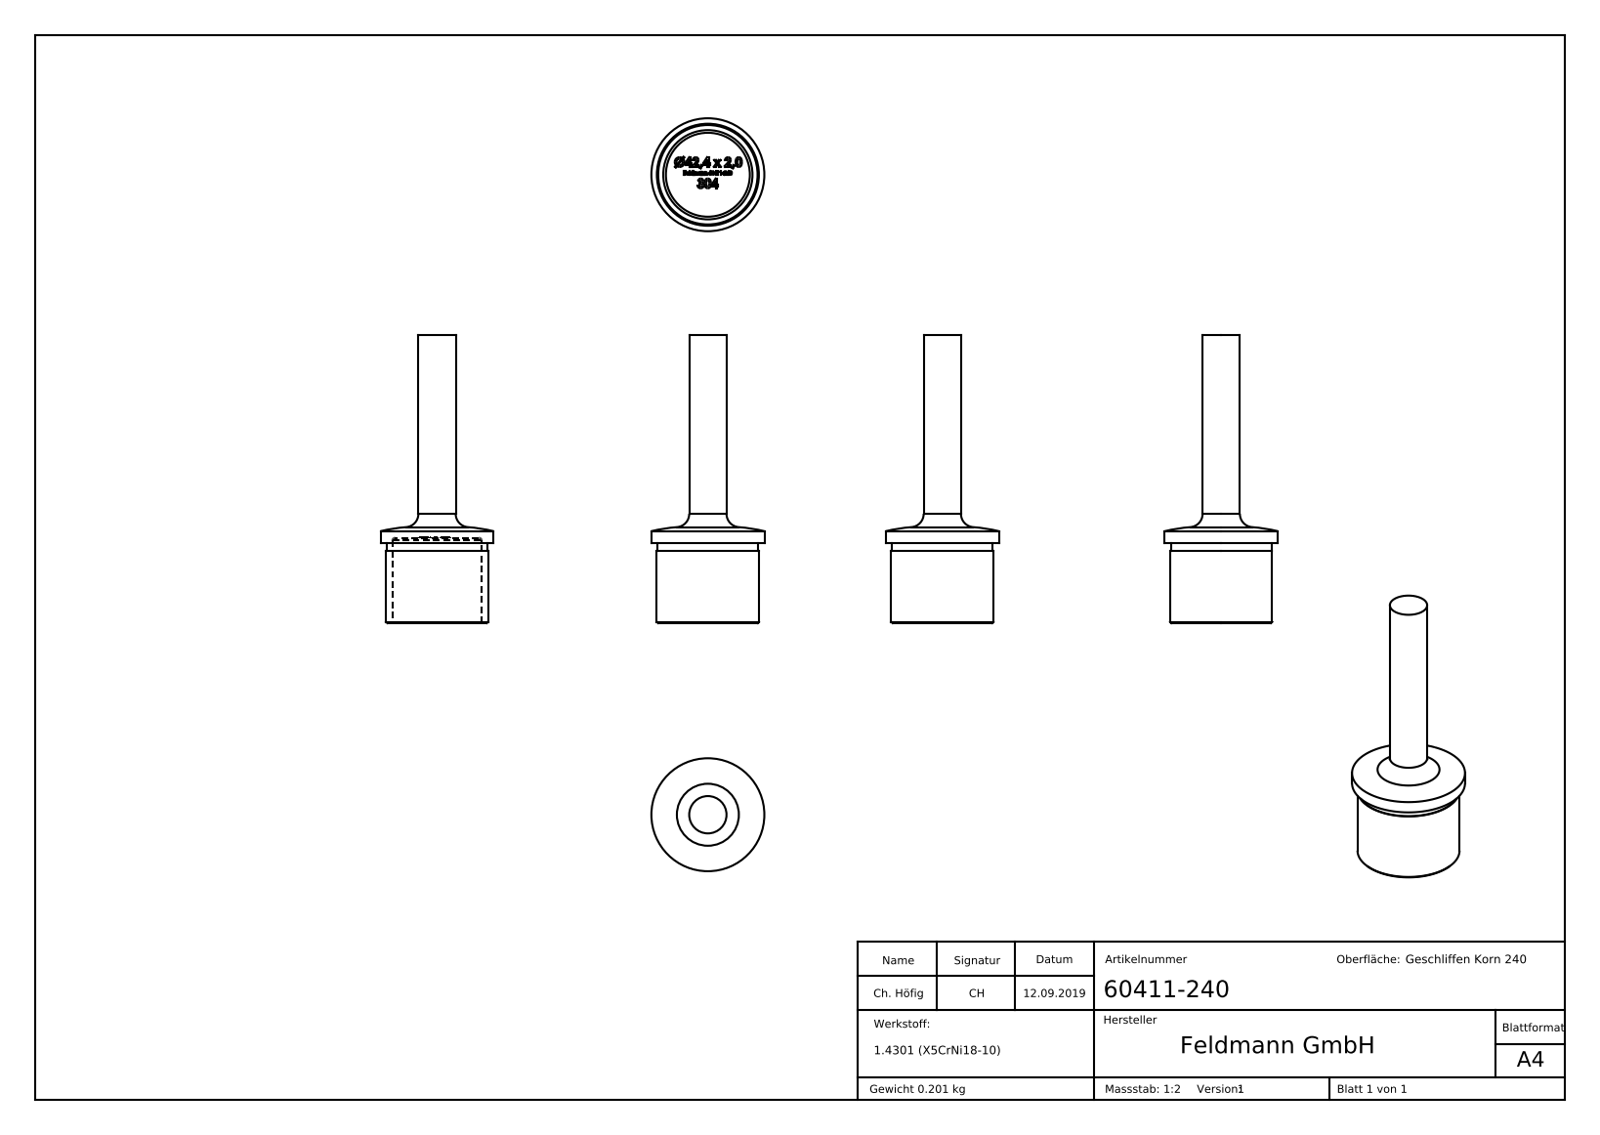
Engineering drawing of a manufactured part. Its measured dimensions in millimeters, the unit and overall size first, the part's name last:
Units: millimetres
Overall size (bounding box): 108 × 42.4 × 42.4
Round holes (diameter × count): ⌀33.5 ×1
Round bosses / shafts (diameter × count): ⌀42.4 ×1, ⌀38.3 ×1, ⌀37.9 ×1, ⌀14 ×1
Main face-to-face distances: 2, 30, 32, 108, 78, 76, 32.1, 2.1, 75.9, 3
Volume: 25 445 mm³ · Surface area: 13 488 mm²
Bodies: 1 solid, 397 faces (241 planar, 10 cylindrical, 146 other)
Part name (STEP PRODUCT): 60411-240
STEP written by: SolidWorks 2015 (CONFIG_CONTROL_DESIGN)
